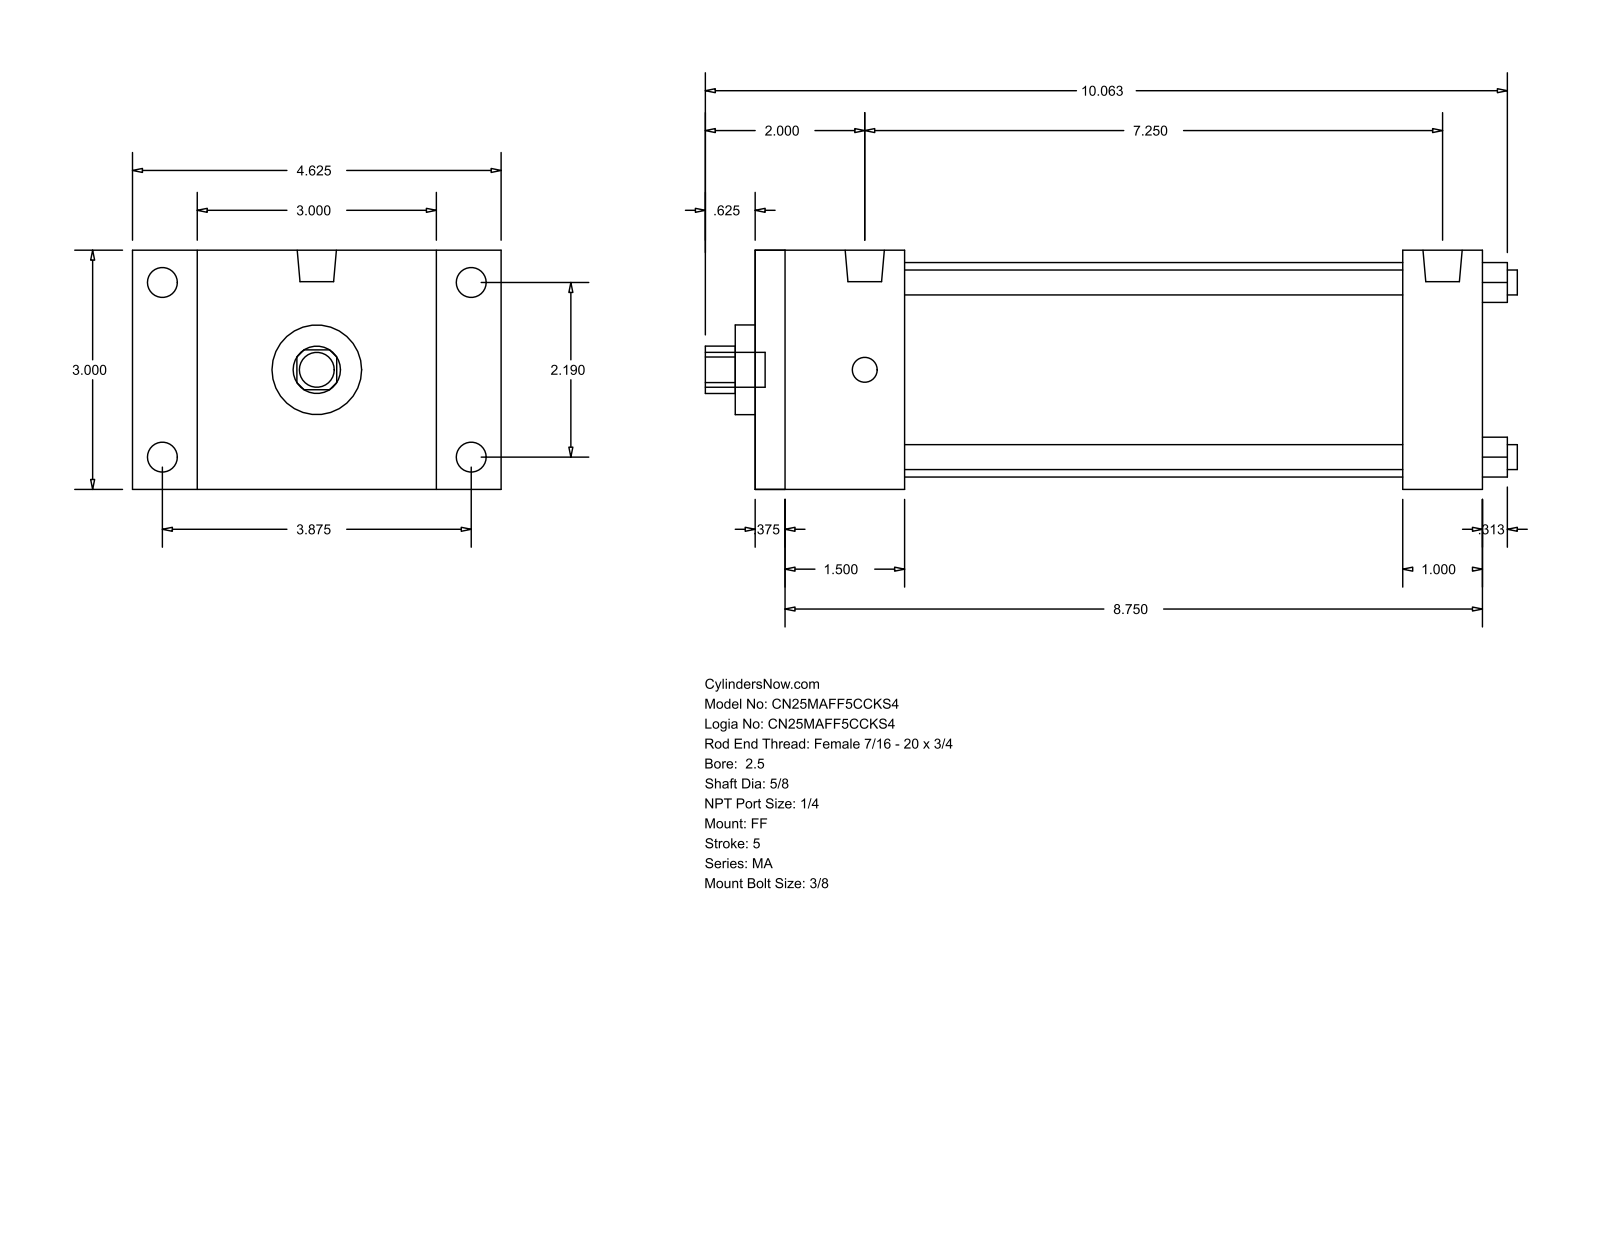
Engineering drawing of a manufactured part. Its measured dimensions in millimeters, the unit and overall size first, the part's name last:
Units: millimetres
Overall size (bounding box): 258.76 × 117.47 × 76.2
Round holes (diameter × count): ⌀7.94 ×4, ⌀15.88 ×1, ⌀28.57 ×1, ⌀68.33 ×1
Round bosses / shafts (diameter × count): ⌀9.53 ×4, ⌀7.94 ×4, ⌀12.49 ×2, ⌀11.11 ×1
Partial cylindrical surfaces — rounded edges, fillets, slot ends (radius × count): R7.54 ×1
Main face-to-face distances: 76.2, 231.77, 9.52, 222.25, 25.4, 47.62, 206.37, 38.1, 196.85, 158.75
Hole centre spacings: 39.33, 55.62, 78.66
Bodies: 0 solids, 92 faces (64 planar, 28 cylindrical, 0 other)
Part name (STEP PRODUCT): MA_FF__0250_0.625
STEP written by: GSSL Pune (CONFIG_CONTROL_DESIGN)
